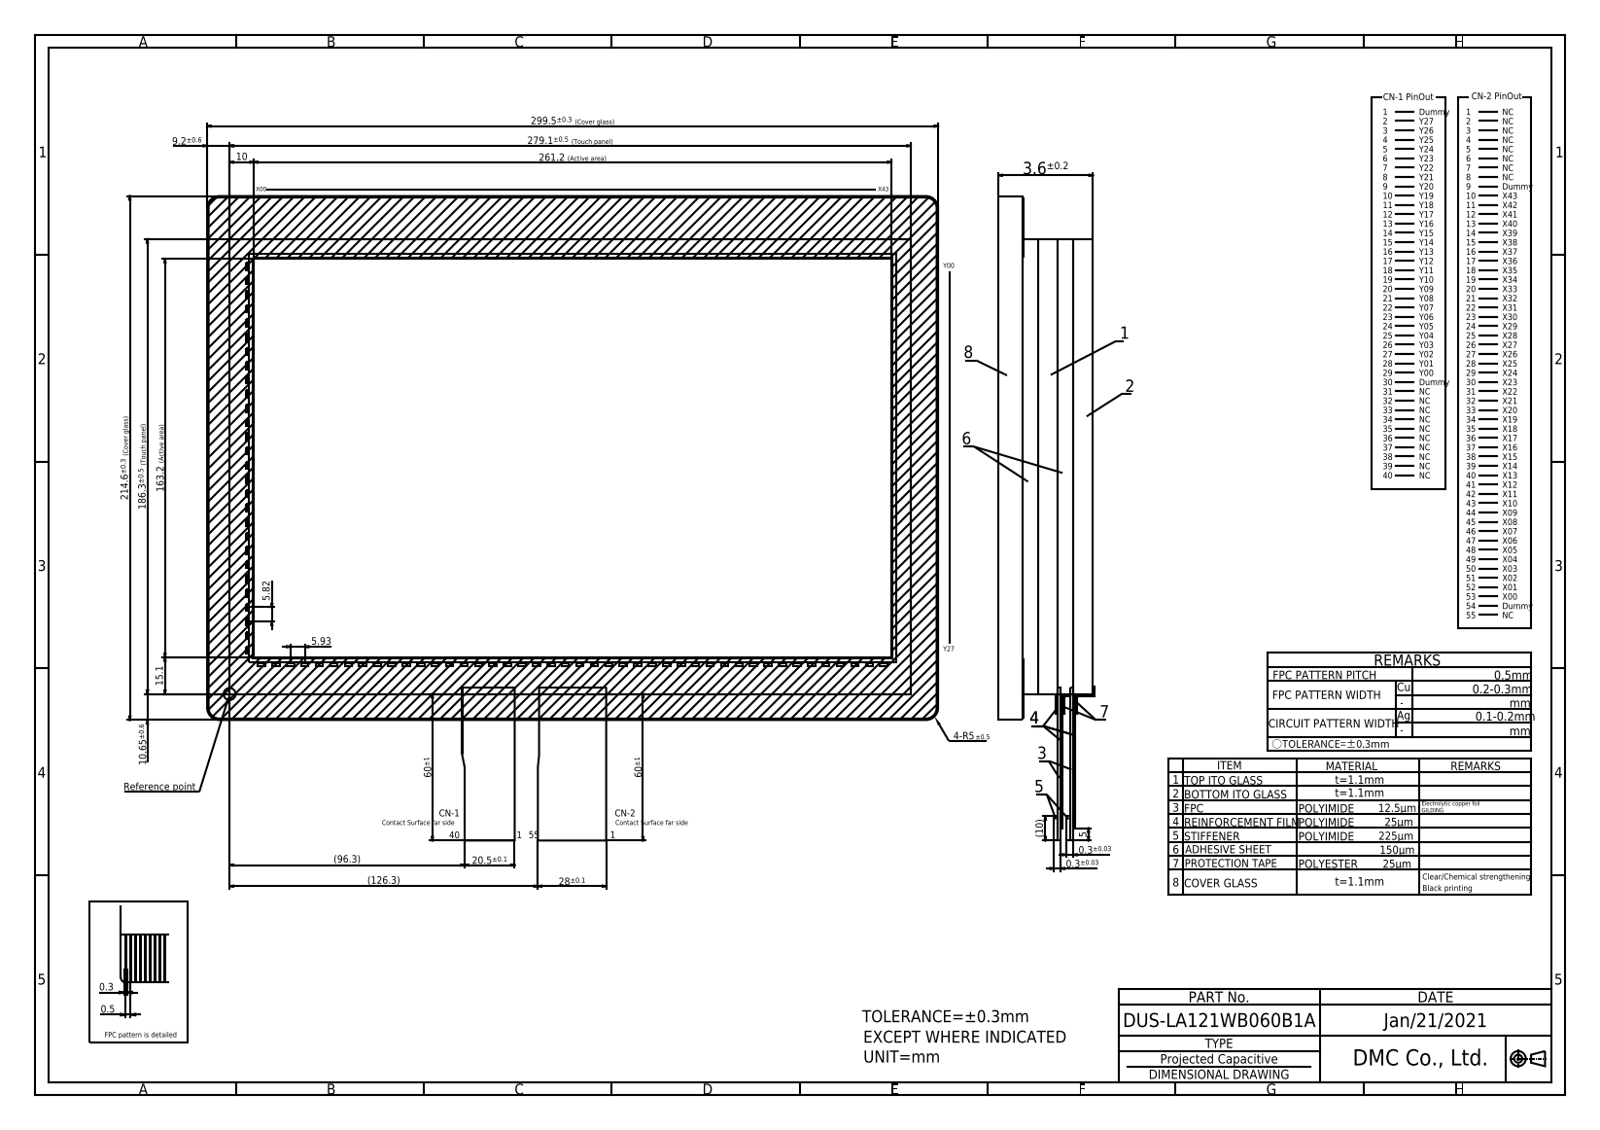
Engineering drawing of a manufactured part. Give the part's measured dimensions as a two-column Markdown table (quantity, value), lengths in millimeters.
| quantity | value |
| --- | --- |
| part name | DUS-LA121WB060B1A |
| STEP written by | Autodesk Inventor 2020 (CONFIG_CONTROL_DESIGN) |
| units | millimeters |
| bodies | 1 solid, 425 faces (420 planar, 5 cylindrical, 0 other) |
| overall size | 419.3 × 306.87 × 3.6 |
| volume | 196 817 mm³ |
| surface area | 223 211 mm² |
| partial cylindrical surfaces (radius × count) | 5 × 4, 0.2 × 1 |
| main face-to-face distances | 1.1, 2.5, 3.6, 1.2, 2.4, 1.25, 1.15, 1.35, 2.45, 2.35 |
